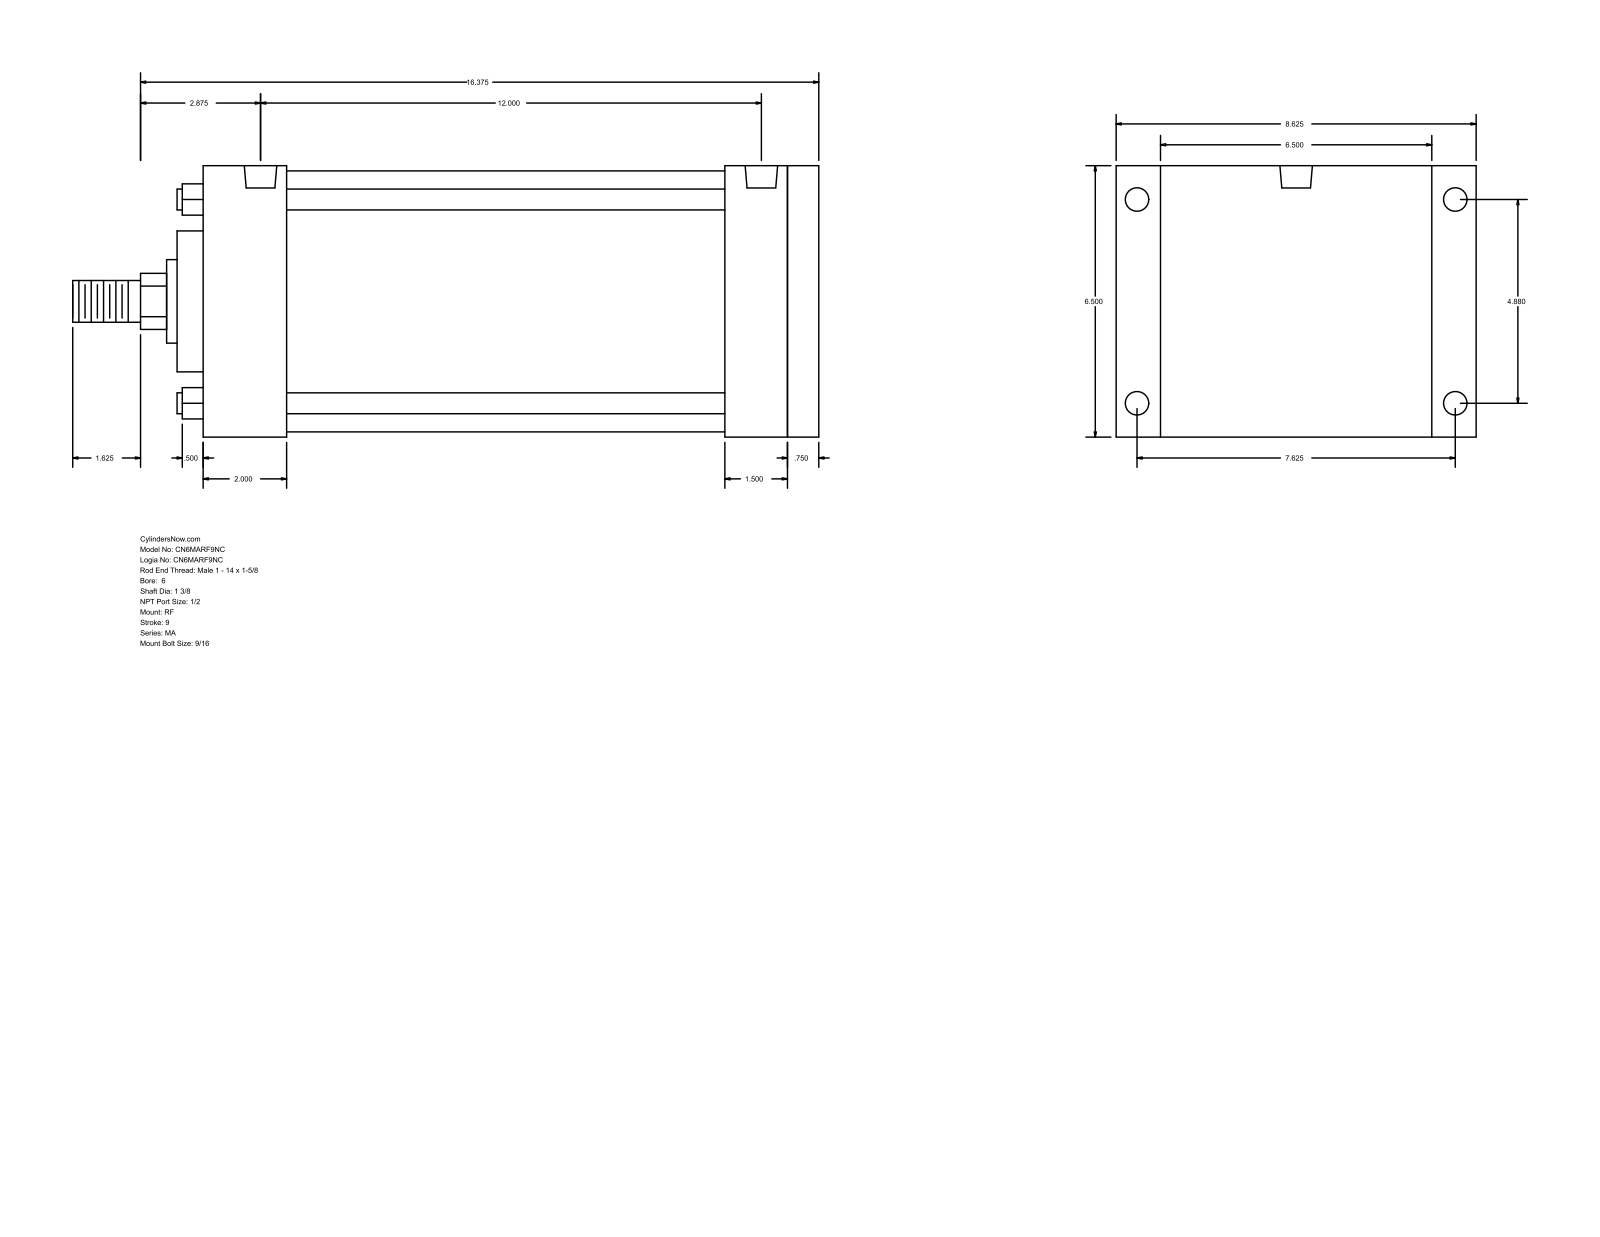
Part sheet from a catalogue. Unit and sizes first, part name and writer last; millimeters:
Units: millimetres
Overall size (bounding box): 457.2 × 219.07 × 165.1
Round holes (diameter × count): ⌀14.29 ×4, ⌀17.46 ×4, ⌀19.77 ×2
Round bosses / shafts (diameter × count): ⌀12.7 ×4, ⌀158.75 ×1, ⌀85.72 ×1, ⌀50.8 ×1, ⌀34.92 ×1, ⌀25.4 ×1
Partial cylindrical surfaces — rounded edges, fillets, slot ends (radius × count): R17.06 ×1
Main face-to-face distances: 165.1, 377.83, 19.05, 358.78, 50.8, 307.98, 327.03, 320.67, 269.87, 38.11
Hole centre spacings: 123.96, 193.68, 229.95, 307.97, 3.18, 304.79
Bodies: 0 solids, 94 faces (65 planar, 29 cylindrical, 0 other)
Part name (STEP PRODUCT): MA_RF__0600_1.375
STEP written by: GSSL Pune (CONFIG_CONTROL_DESIGN)
